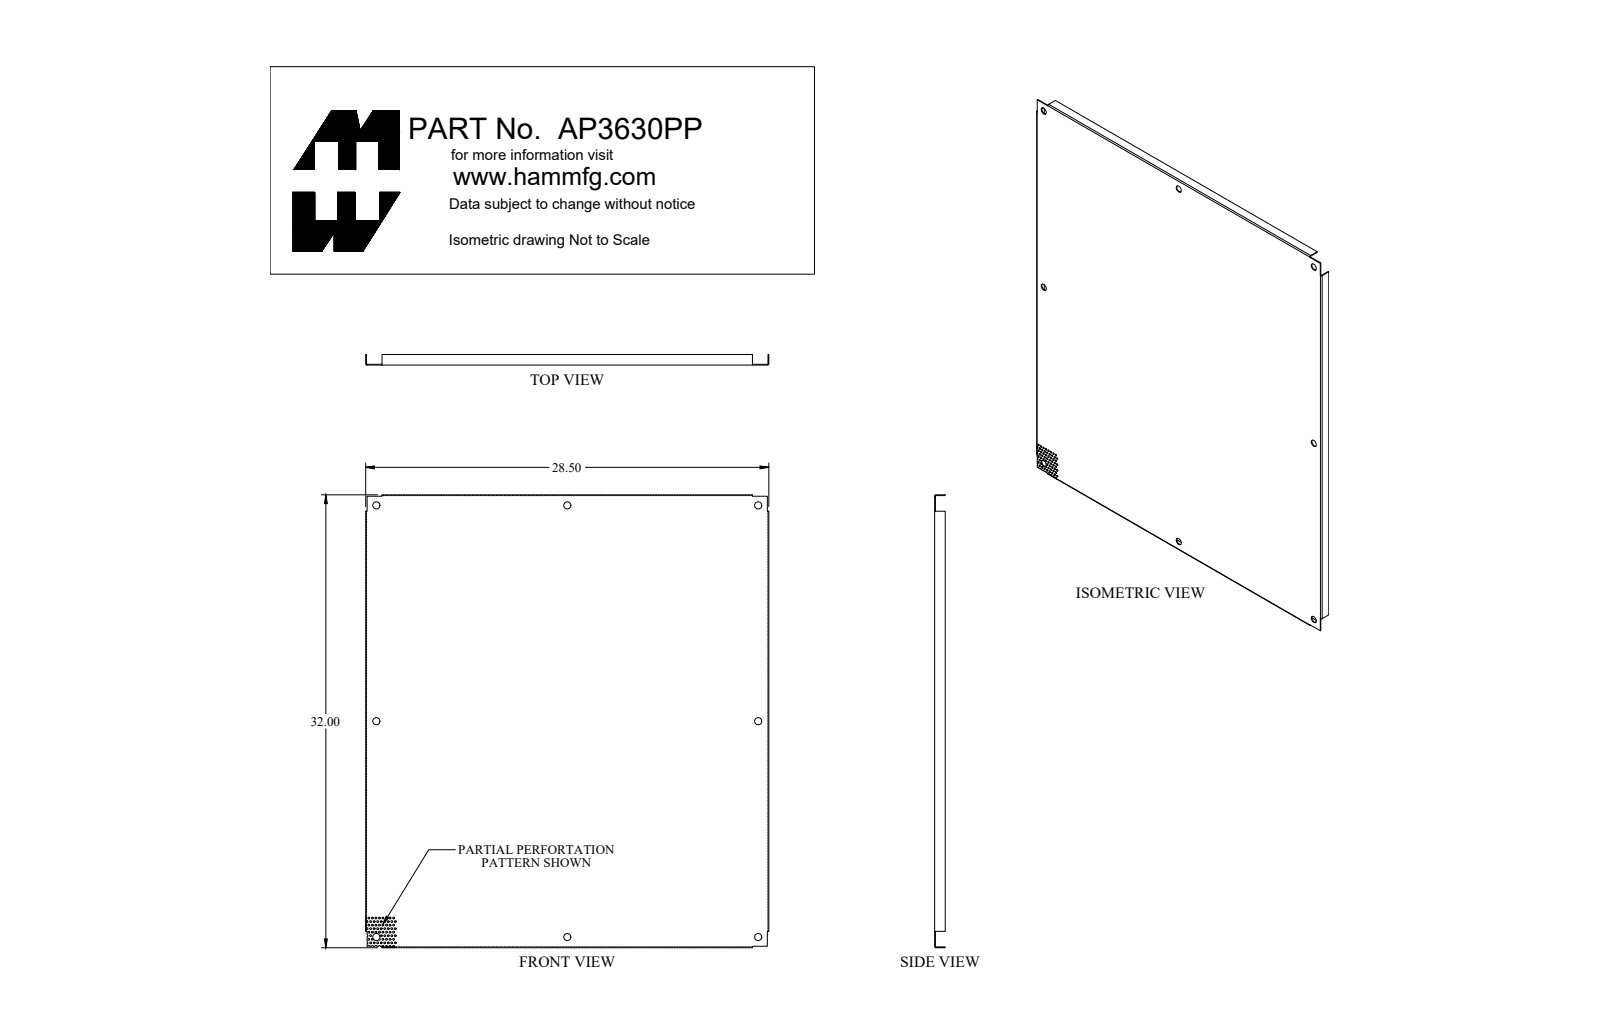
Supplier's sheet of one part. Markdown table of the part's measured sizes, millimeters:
| quantity | value |
| --- | --- |
| part name | AP3630PP_Default |
| STEP written by | SolidWorks 2019 (CONFIG_CONTROL_DESIGN) |
| units | millimeters |
| bodies | 1 solid, 268 faces (43 planar, 217 cylindrical, 8 other) |
| overall size | 812.8 × 723.9 × 19.1 |
| volume | 918 300 mm³ |
| surface area | 1 275 000 mm² |
| round holes (diameter × count) | 3.2 × 74, 12.7 × 8, 3.2 × 2 |
| partial cylindrical surfaces (radius × count) | 1.6 × 15, 1.6 × 6, 0.7 × 4, 2.2 × 4 |
| main face-to-face distances | 1.4, 722.5, 811.4, 721, 723.9, 812.8, 809.9, 19.1, 17.6, 2.6 |
| hole center spacings | 7.1, 12.7, 6.4, 14.2, 11.5, 19.3, 17.1, 19.1 |
